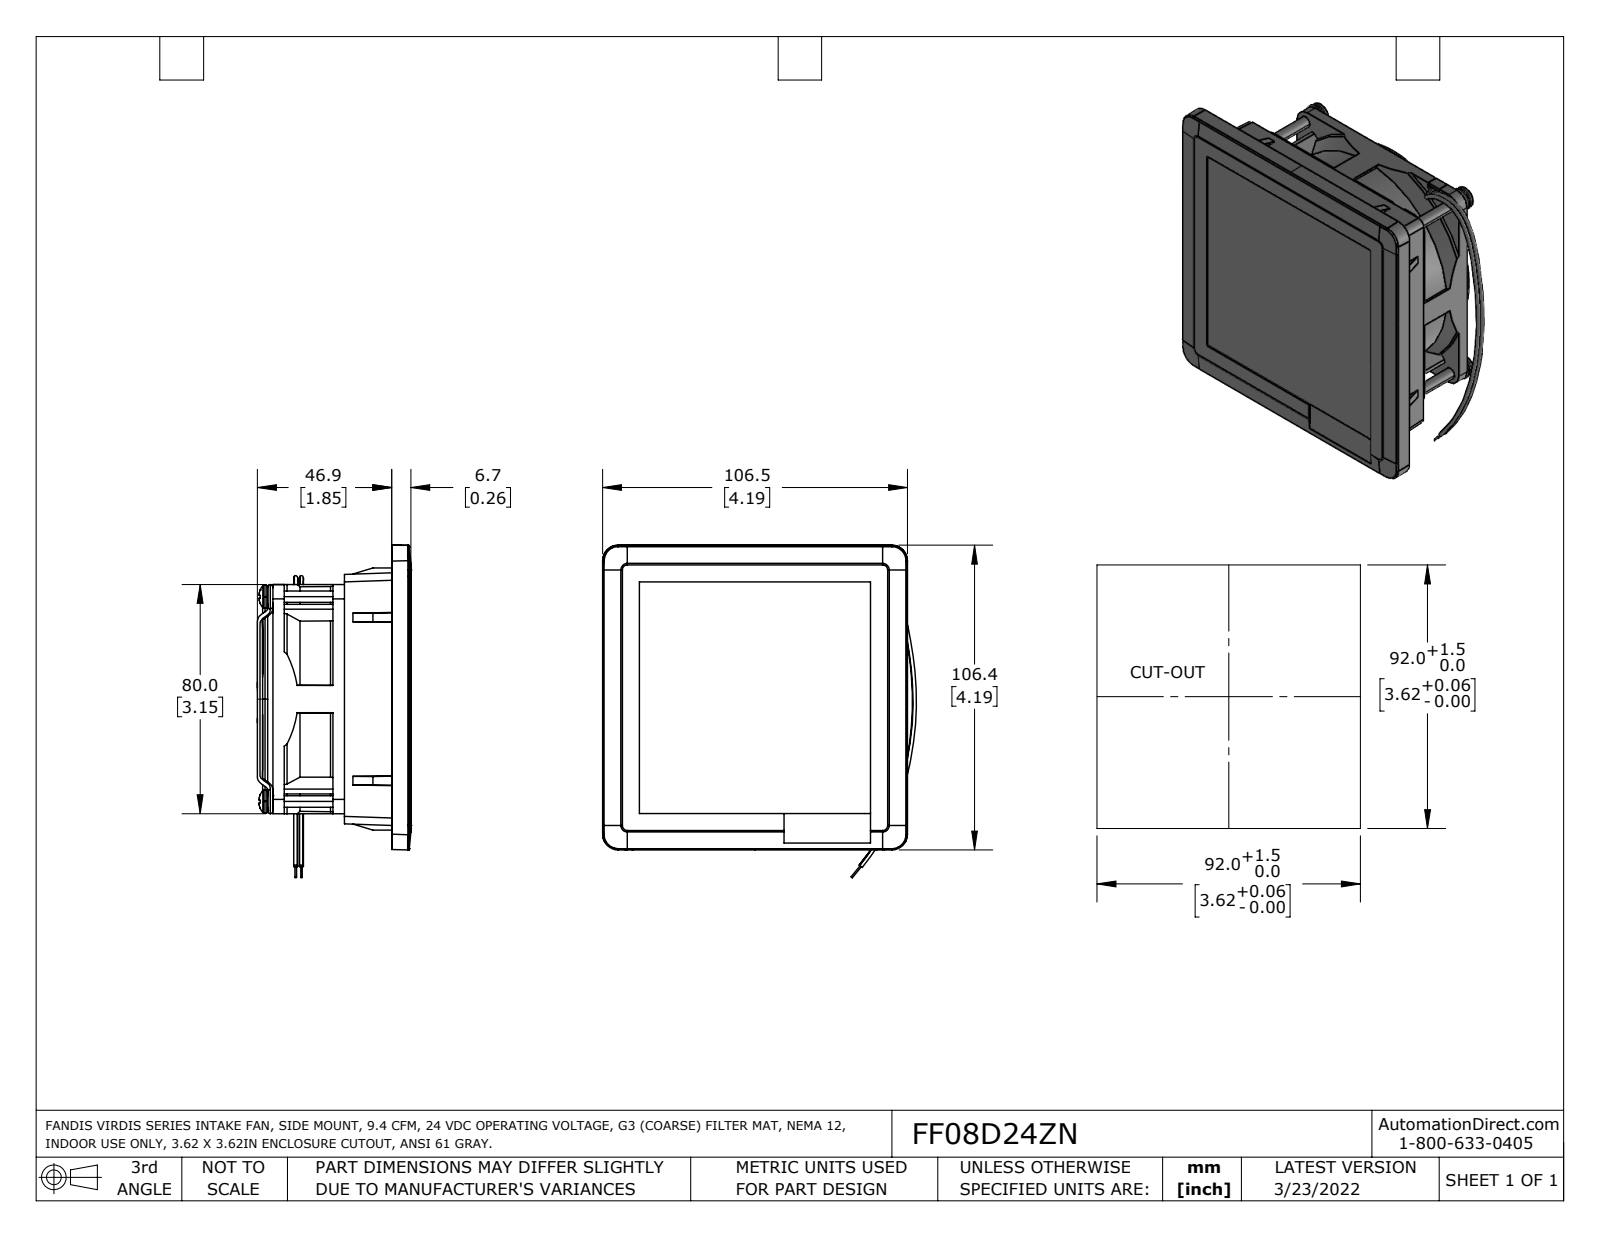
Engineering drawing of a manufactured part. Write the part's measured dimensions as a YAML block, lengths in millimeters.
part_name: "FF08D24UN"
step_written_by: "SolidWorks 2021 (AUTOMOTIVE_DESIGN)"
units: millimeters
bodies: {solids: 12, faces: 473, planar: 214, cylindrical: 79, other: 180}
overall_size: [116.1, 109.6, 53.6]
volume: 338200
surface_area: 50910
round_holes:
  - {diameter: 4.3, count: 4}
round_bosses_or_shafts:
  - {diameter: 8, count: 4}
  - {diameter: 4, count: 4}
  - {diameter: 0.5, count: 2}
partial_cylinders:
  - {radius: 0.5, count: 7}
  - {radius: 1, count: 4}
  - {radius: 1.5, count: 4}
  - {radius: 2.6, count: 4}
  - {radius: 5, count: 4}
  - {radius: 6, count: 4}
face_to_face_distances: [47.7, 4, 21, 0.5, 48.2, 80, 18, 22, 23.2, 22.7]
hole_center_spacings: [71.5, 101.1]
